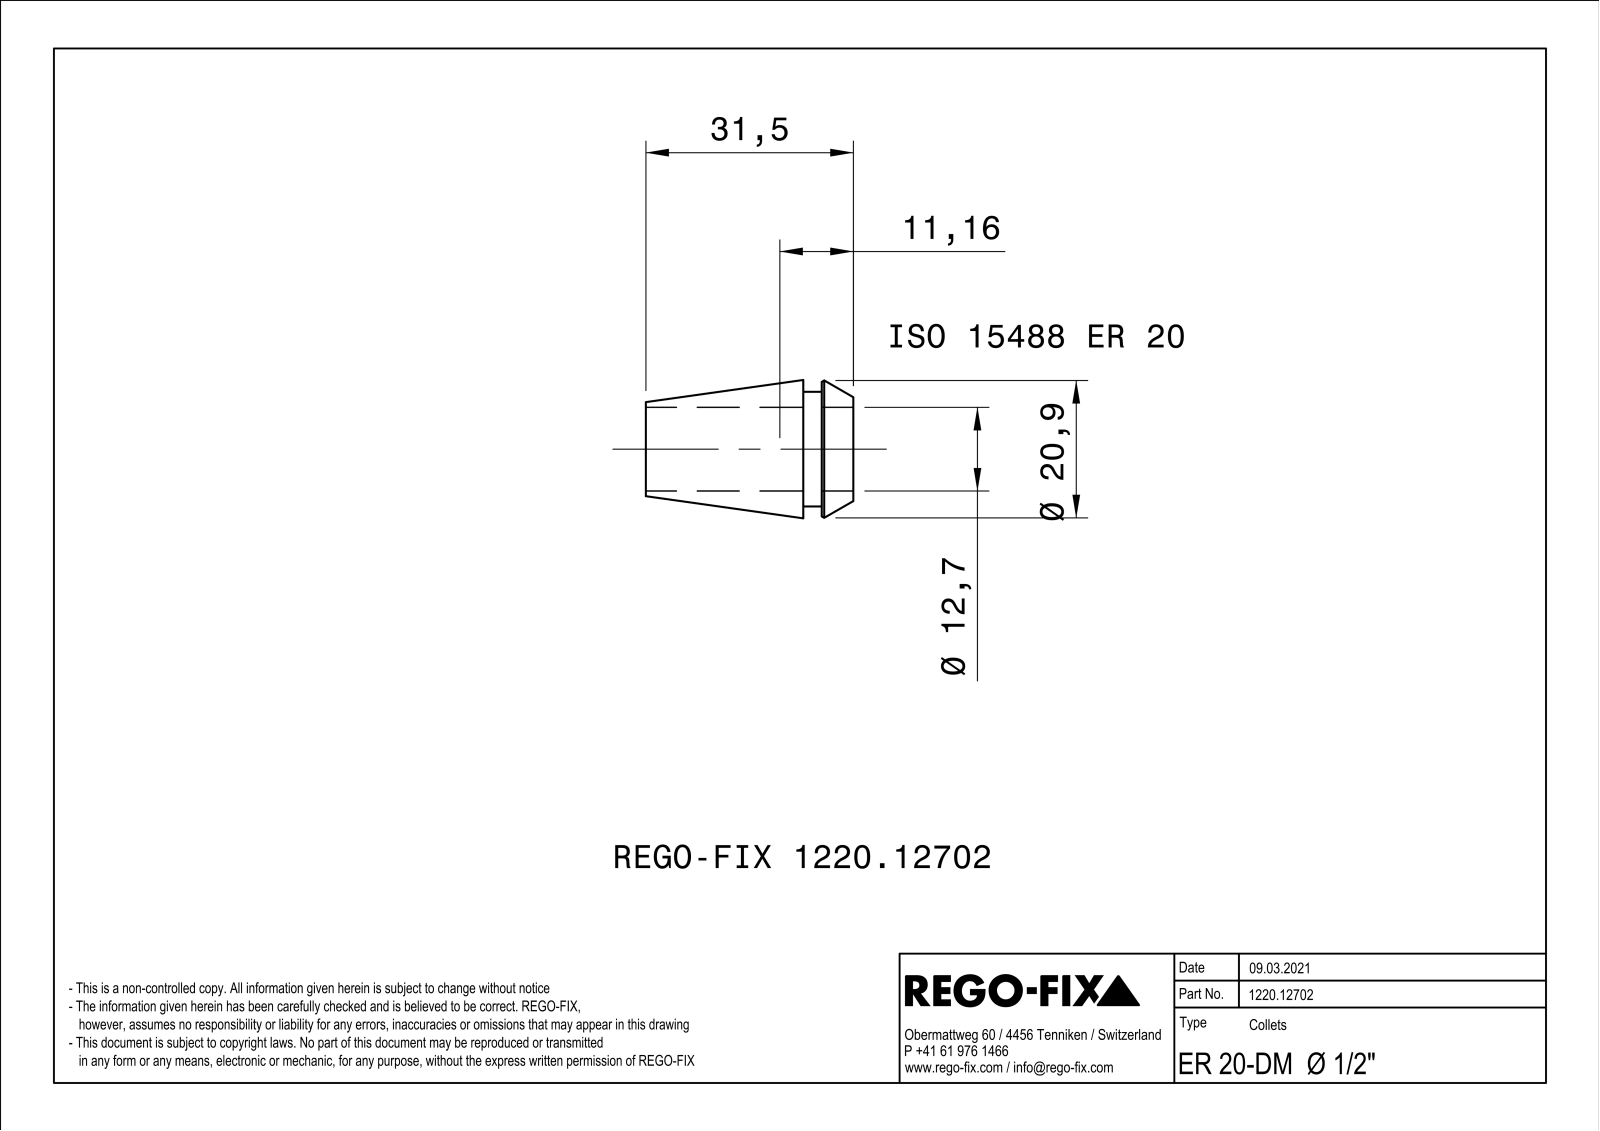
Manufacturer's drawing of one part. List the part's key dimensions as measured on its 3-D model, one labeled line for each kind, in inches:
Part name (STEP PRODUCT): NOCUT
STEP written by: SIEMENS PLM Software Solid Edge ST10 (AUTOMOTIVE_DESIGN)
Units: inches
Bodies: 1 solid, 154 faces (80 planar, 9 cylindrical, 65 other)
Overall size (bounding box): 1.24 × 0.826 × 0.826
Volume: 0.194 in³ · Surface area: 7.012 in²
Round holes (diameter × count): ⌀0.5 ×1
Round bosses / shafts (diameter × count): ⌀0.685 ×1
Main face-to-face distances: 0.031, 0.11, 0.189, 0.299, 0.551, 0.362, 0.252, 1.24, 1.051, 0.941
